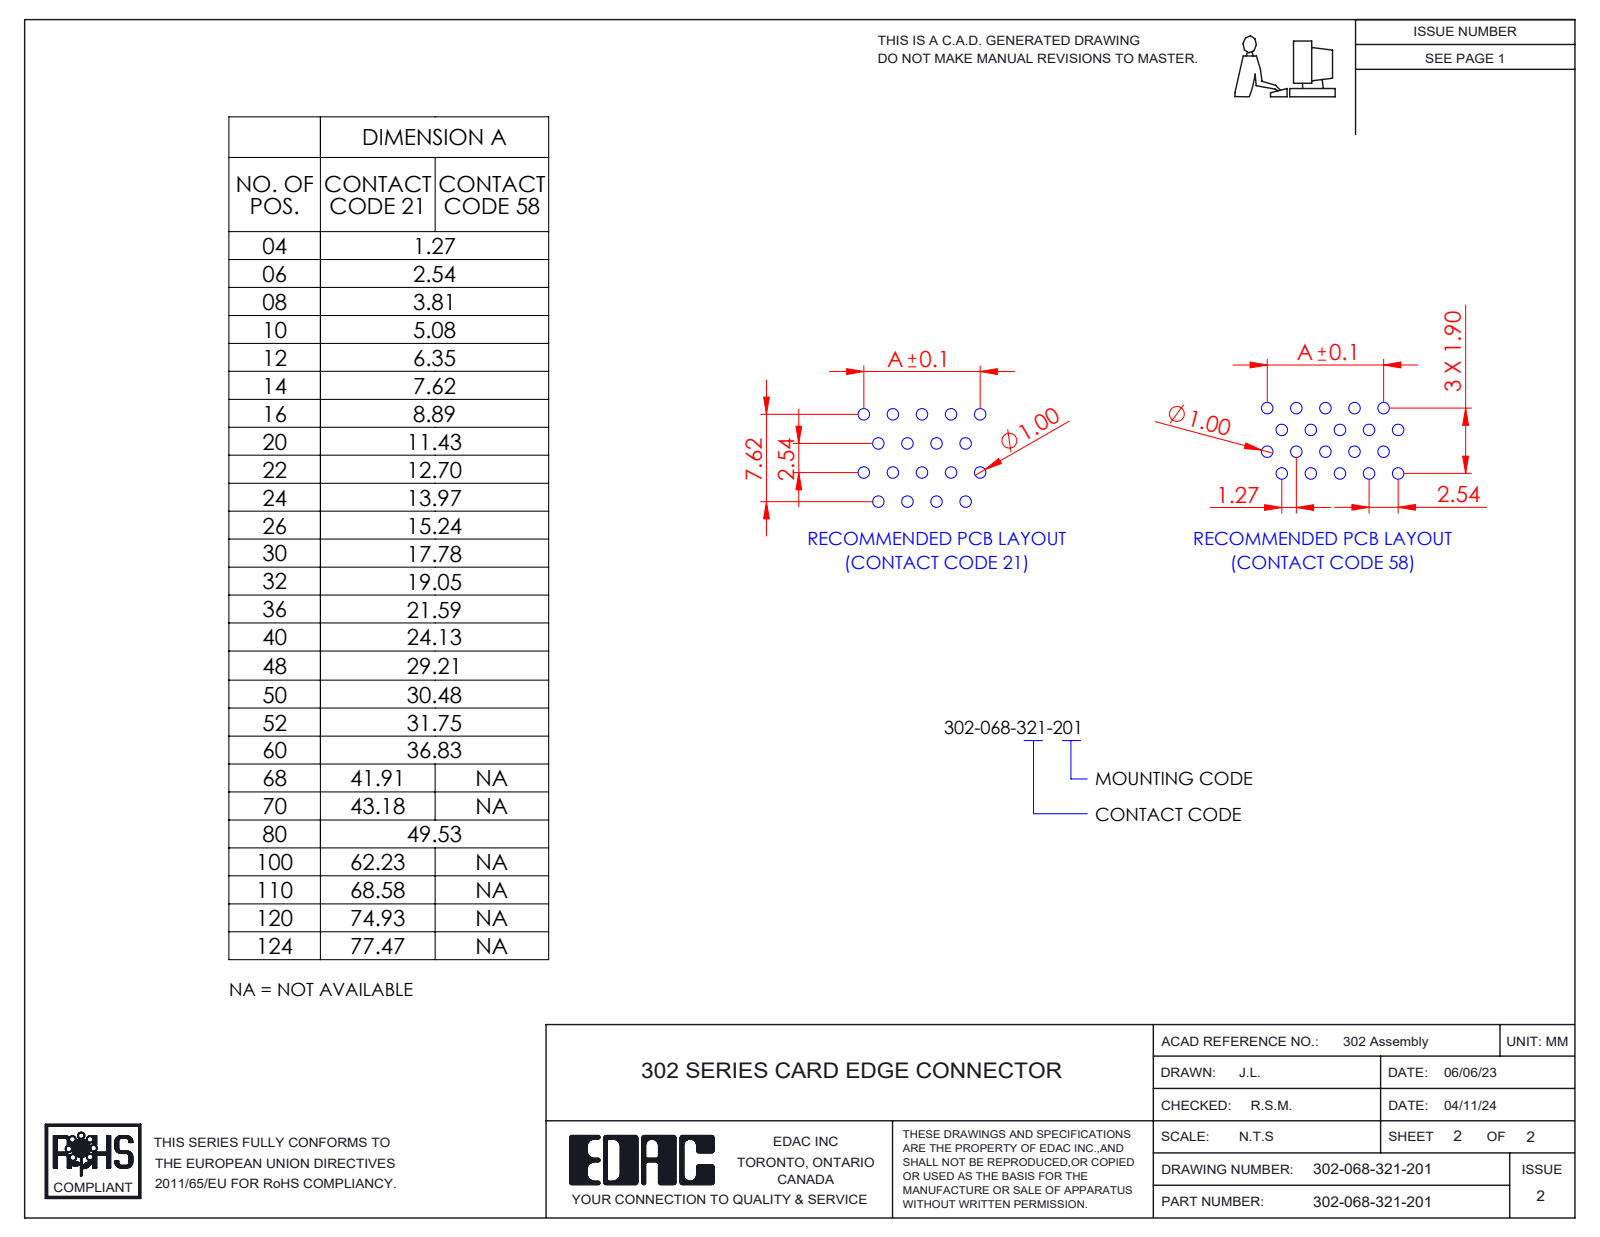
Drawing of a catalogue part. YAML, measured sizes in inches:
part_name: "Contact_302-290-X21 (1); Contact_302-290-X21 (2); HSG_Vertical HSG; 302-068-321-201"
step_written_by: "SolidWorks 2023 (CONFIG_CONTROL_DESIGN)"
units: inches
bodies: {solids: 69, faces: 3160, planar: 2327, cylindrical: 693, other: 140}
overall_size: [1.94, 0.694, 0.35]
volume: 0.234
surface_area: 16.21
partial_cylinders:
  - {radius: 0.008, count: 76}
  - {radius: 0.08, count: 4}
  - {radius: 0.082, count: 4}
  - {radius: 0.004, count: 2}
  - {radius: 0.016, count: 2}
  - {radius: 0.016, count: 2}
  - {radius: 0.049, count: 2}
  - {radius: 0.06, count: 2}
face_to_face_distances: [0.1, 0.05, 0.2, 0.15, 0.3, 0.25, 0.35, 0.35, 0.4, 0.45]
